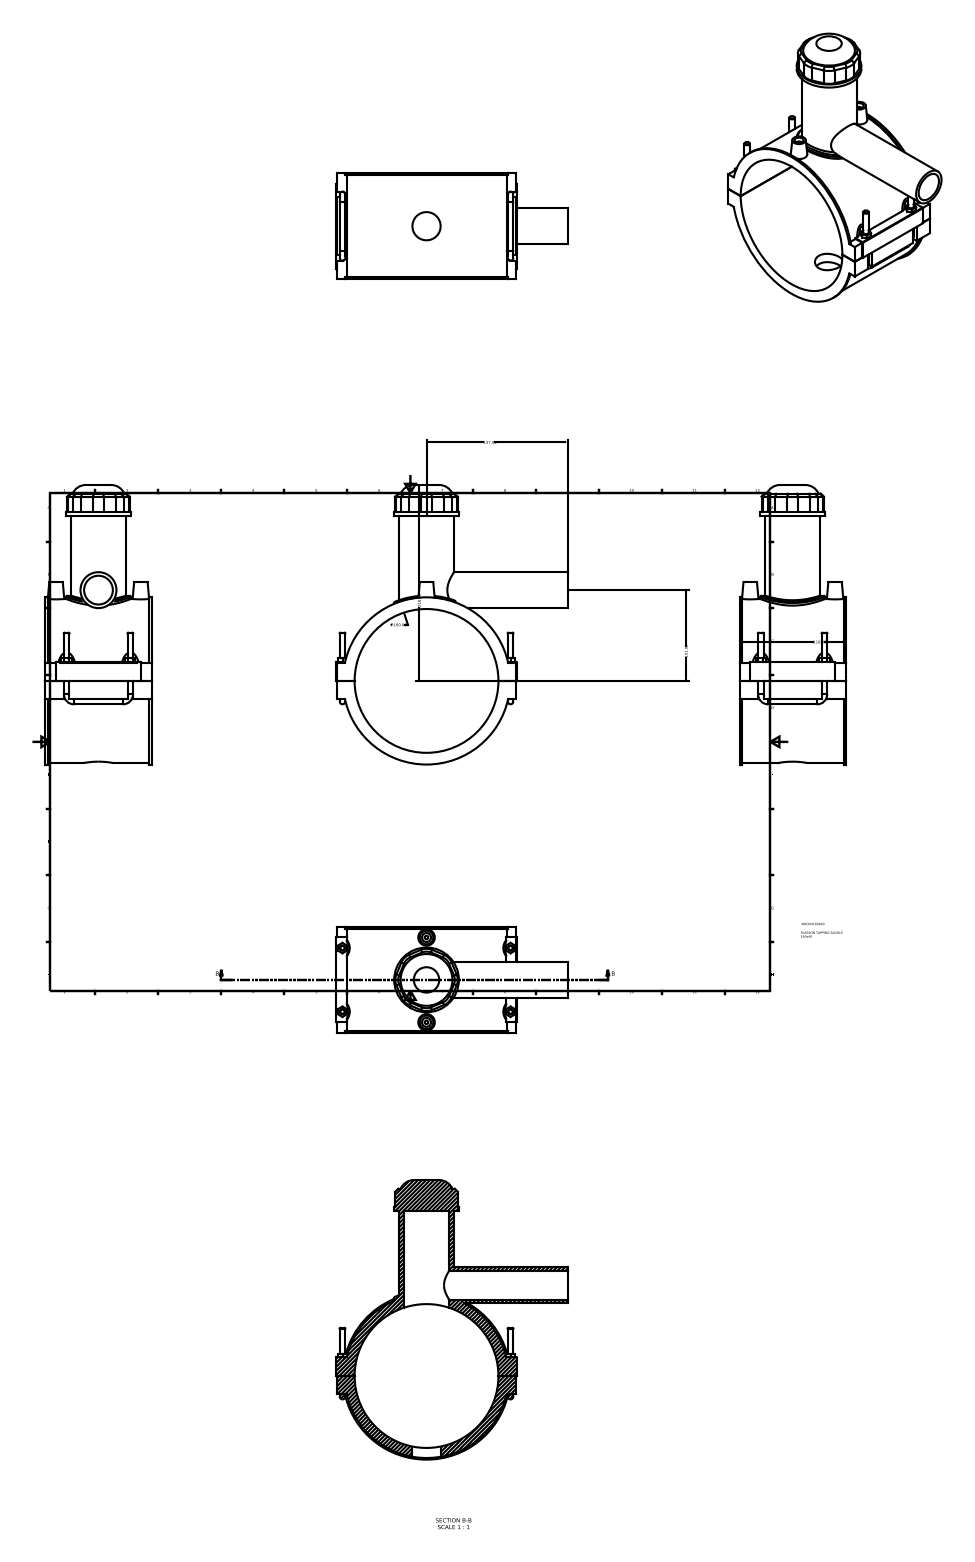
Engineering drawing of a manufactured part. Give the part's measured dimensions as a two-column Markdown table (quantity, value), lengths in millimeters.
| quantity | value |
| --- | --- |
| part name | 496304160040 |
| STEP written by | Autodesk Inventor 2015 (AUTOMOTIVE_DESIGN) |
| units | millimeters |
| bodies | 1 solid, 181 faces (110 planar, 47 cylindrical, 24 other) |
| overall size | 311.02 × 257.5 × 118 |
| volume | 1 043 000 mm³ |
| surface area | 238 848 mm² |
| round holes (diameter × count) | 10 × 2, 31.36 × 1, 32 × 1, 50.4 × 1, 160 × 1 |
| round bosses / shafts (diameter × count) | 6 × 6, 4 × 2, 186.05 × 1, 182.4 × 1, 72 × 1, 61.2 × 1, 40 × 1 |
| partial cylindrical surfaces (radius × count) | 16 × 8, 3 × 4, 7.5 × 4, 0.5 × 1, 94.85 × 1 |
| main face-to-face distances | 118, 1, 200, 183.55, 183.45, 199, 19.95, 20.05, 203.5, 201 |
| hole center spacings | 47.2, 94.4 |
